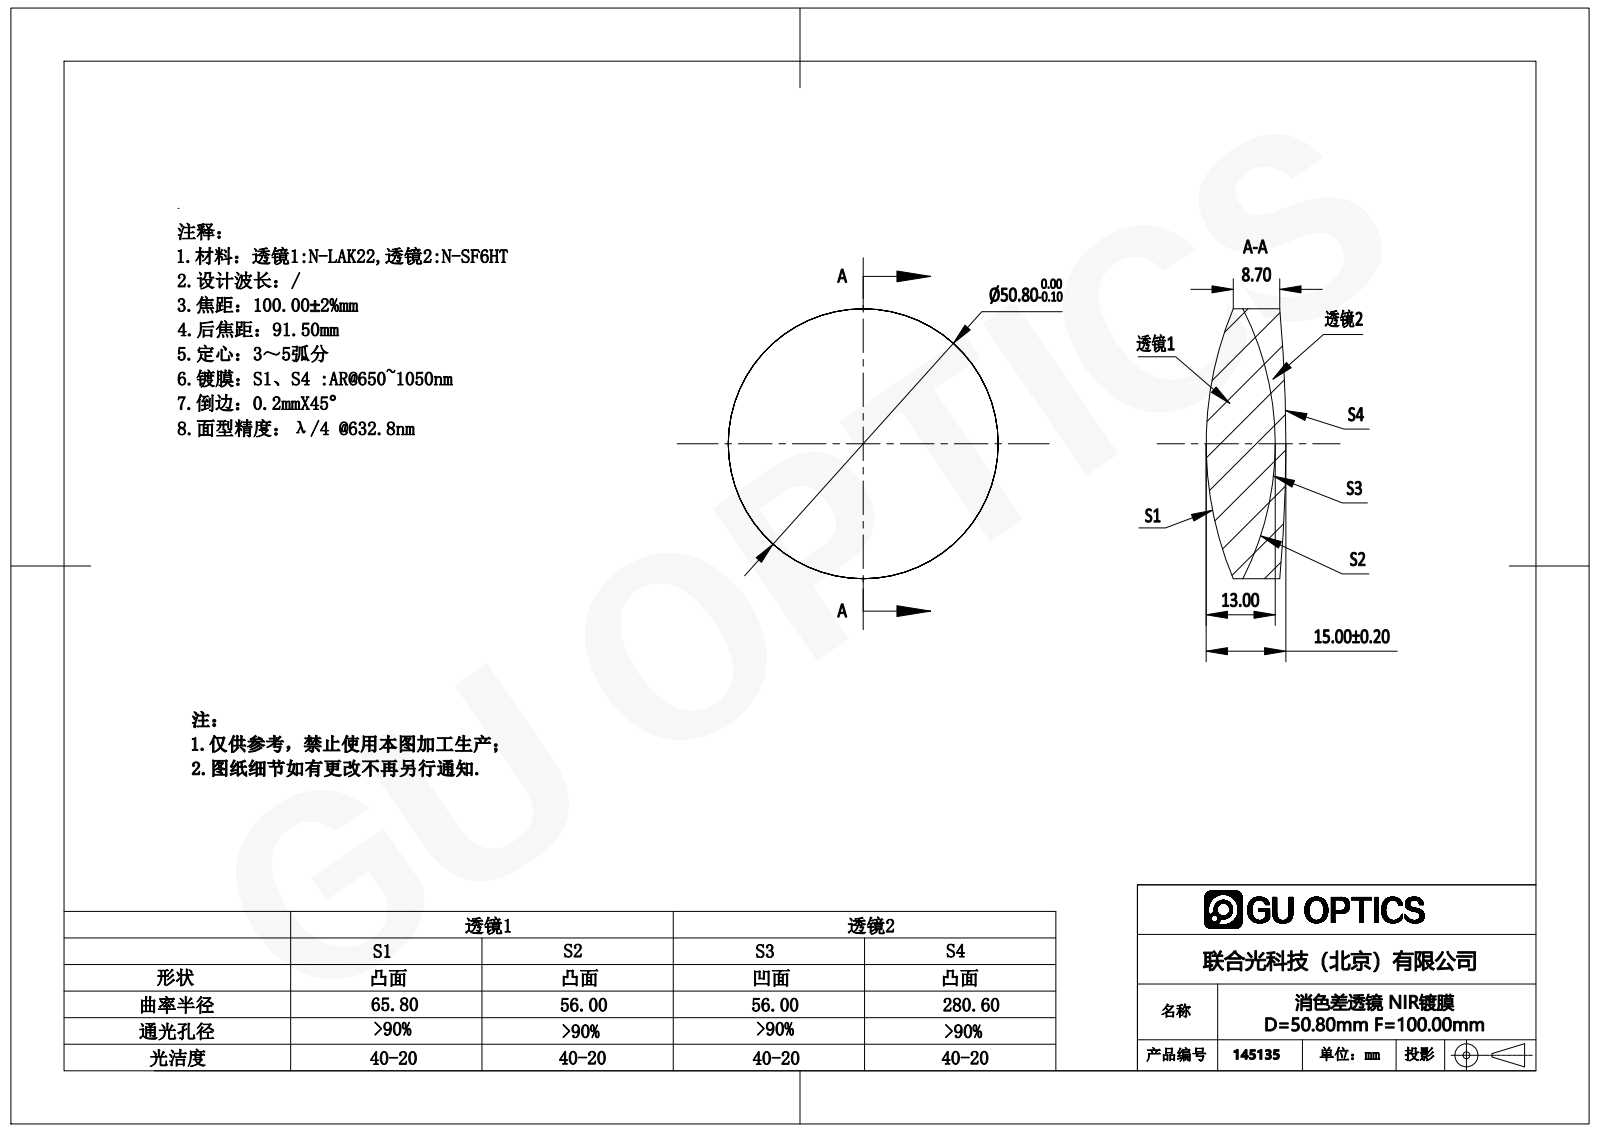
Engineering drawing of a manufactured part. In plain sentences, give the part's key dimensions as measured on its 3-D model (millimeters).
The part is named "145135". Its 3-D file was written by "SolidWorks 2016 (AUTOMOTIVE_DESIGN)". It is 2 solids with 12 faces: 0 planar, 4 cylindrical and 8 other. Overall it measures 50.8 by 50.8 by 15 millimeters. Its volume is 24 137 cubic millimeters and its surface area 9 822 square millimeters. Round bosses or shafts: 1 of diameter 50.8.
